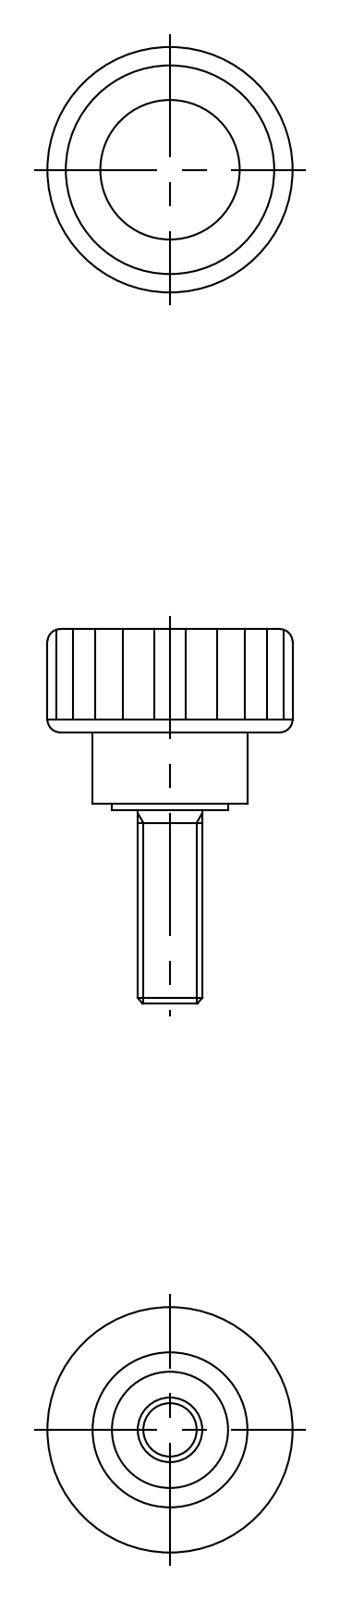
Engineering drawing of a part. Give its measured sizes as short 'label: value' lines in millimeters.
name: screw; knob; KIMS_19_M5_15_3970_36
written by: CADfix (AUTOMOTIVE_DESIGN)
unit: mm
bodies: 2 solids, 32 faces (0 planar, 0 cylindrical, 32 other)
size: 29 × 19 × 19
volume: 2 143 mm³; area: 2 131 mm²
